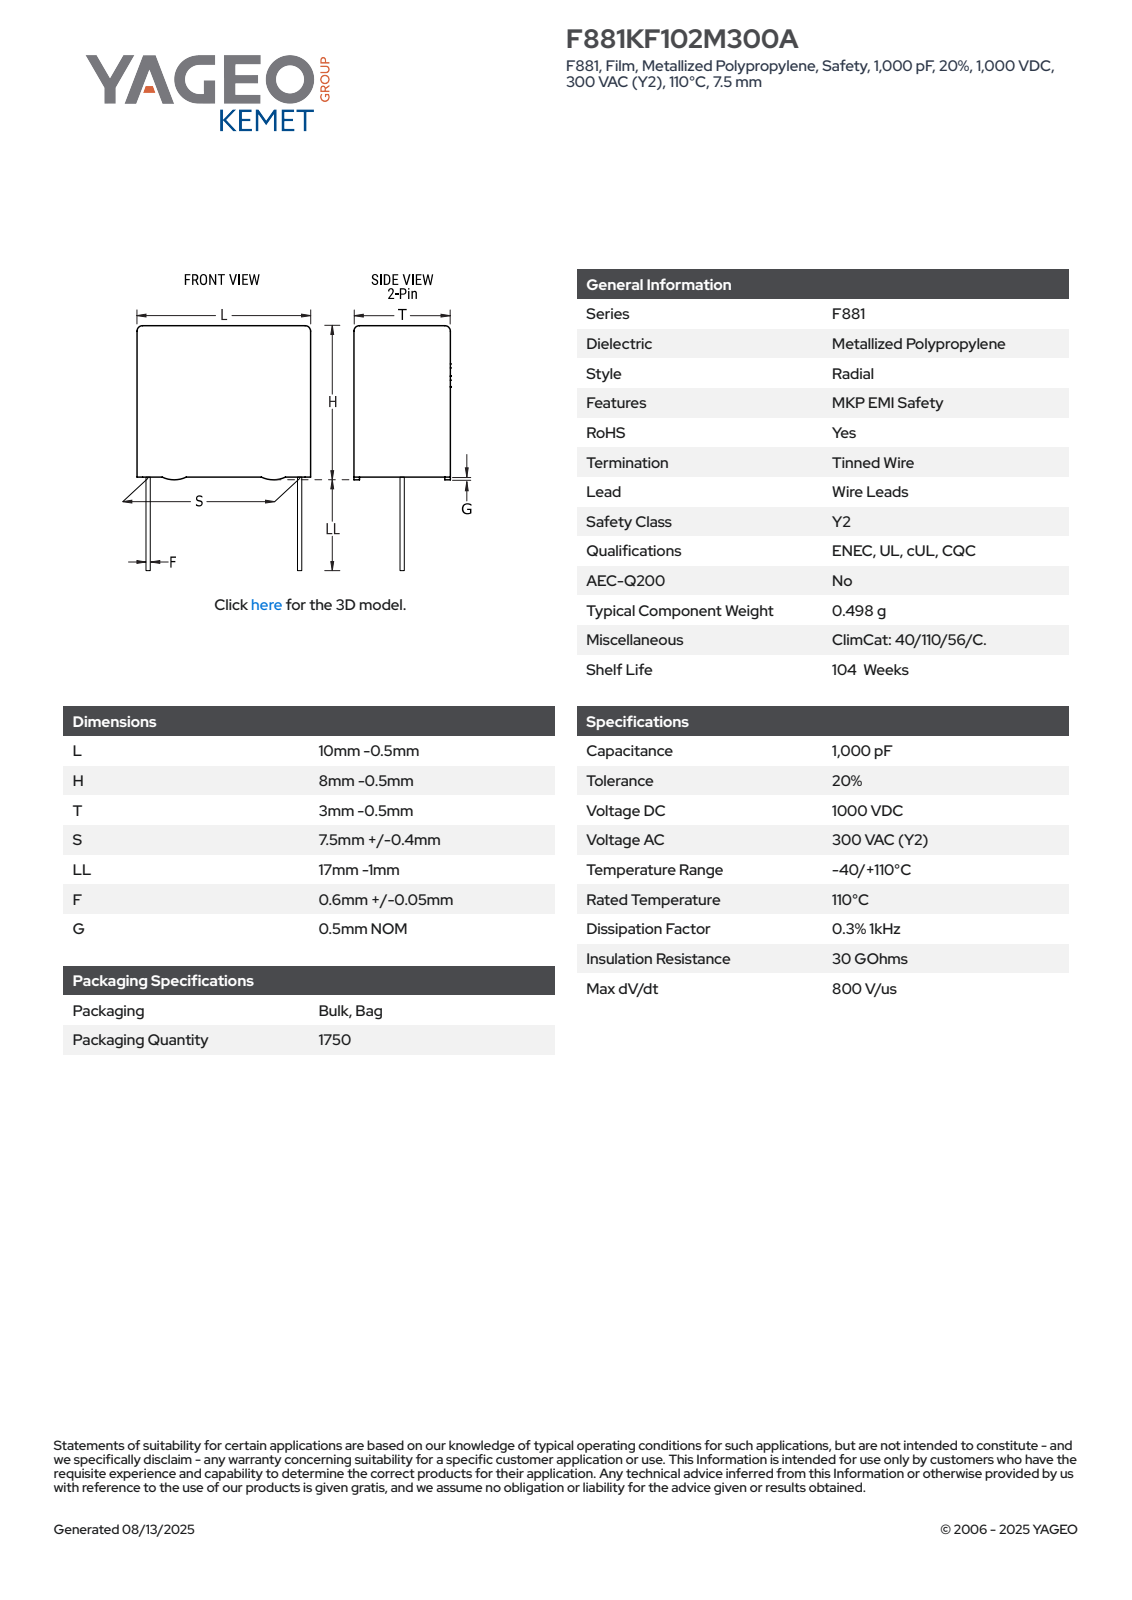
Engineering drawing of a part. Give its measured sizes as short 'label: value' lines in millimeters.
name: CFR_RBG_10X8X3_L9.5H7.5T2.5S7.5LL16F0.65G0.5
written by: SolidWorks 2014 (AUTOMOTIVE_DESIGN)
unit: mm
bodies: 4 solids, 89 faces (81 planar, 8 cylindrical, 0 other)
size: 23.5 × 9.5 × 2.5
volume: 176 mm³; area: 294 mm²
bosses: 2× ⌀0.65
rounds: 4× R0.5
face distances: 2.5, 9.5, 7, 2.36, 2.22, 0.5, 7.5, 16, 16.5, 23.5
